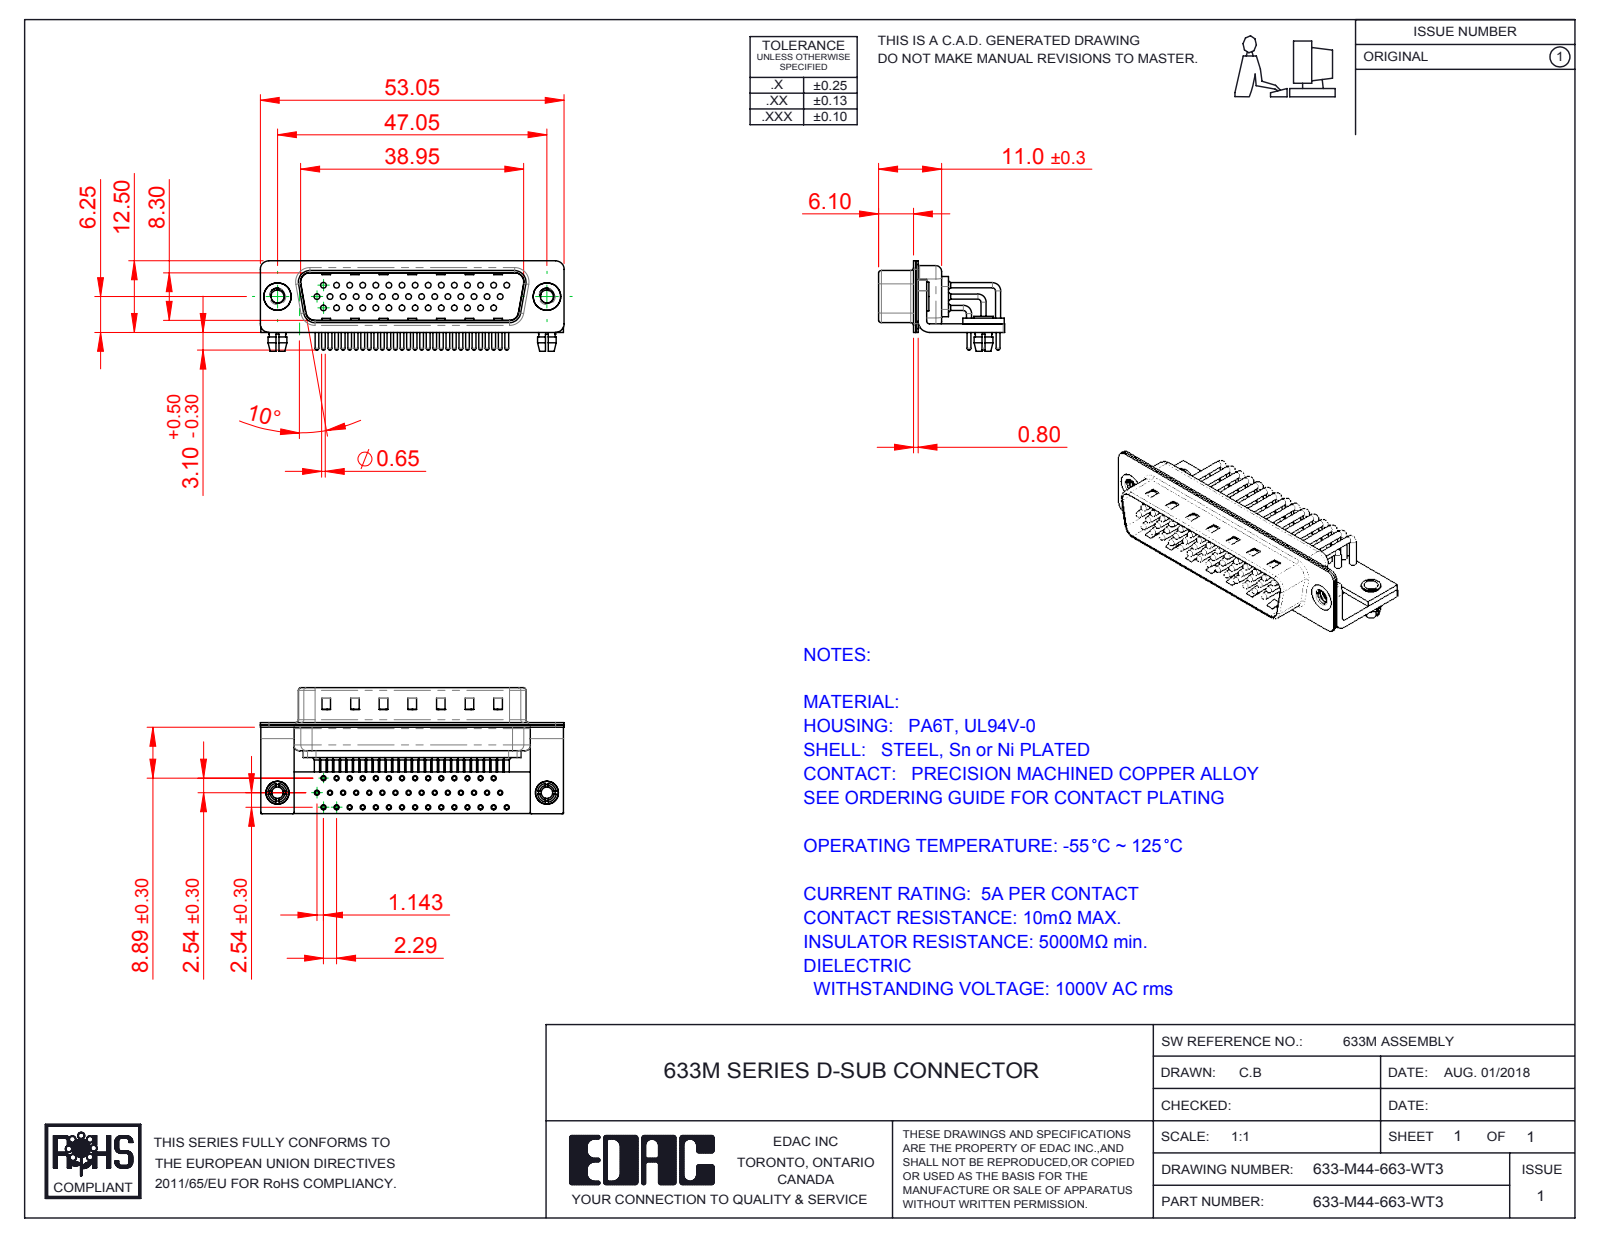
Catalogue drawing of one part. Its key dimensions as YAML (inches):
part_name: "633M Board Lock; 633M Stabilizer Board_44 Contacts; 633M Stabilizer Bracket; 633M 4-40 Threaded Rivet_Stabilizer (+7 more)"
step_written_by: "SolidWorks 2016 (CONFIG_CONTROL_DESIGN)"
units: inches
bodies: {solids: 54, faces: 5446, planar: 3061, cylindrical: 1863, other: 522}
overall_size: [2.089, 0.866, 0.622]
volume: 0.232
surface_area: 18.37
round_holes:
  - {diameter: 0.079, count: 46}
  - {diameter: 0.035, count: 44}
  - {diameter: 0.039, count: 44}
  - {diameter: 0.067, count: 44}
  - {diameter: 0.089, count: 2}
  - {diameter: 0.098, count: 2}
  - {diameter: 0.126, count: 2}
  - {diameter: 0.157, count: 2}
  - {diameter: 0.189, count: 2}
round_bosses_or_shafts:
  - {diameter: 0.035, count: 45}
  - {diameter: 0.059, count: 44}
  - {diameter: 0.026, count: 44}
  - {diameter: 0.197, count: 2}
  - {diameter: 0.193, count: 2}
  - {diameter: 0.157, count: 2}
  - {diameter: 0.134, count: 2}
  - {diameter: 0.13, count: 2}
partial_cylinders:
  - {radius: 0.04, count: 44}
  - {radius: 0.01, count: 16}
  - {radius: 0.059, count: 16}
  - {radius: 0.079, count: 13}
  - {radius: 0.02, count: 9}
  - {radius: 0.063, count: 8}
  - {radius: 0.024, count: 4}
  - {radius: 0.026, count: 4}
face_to_face_distances: [0.016, 0.059, 0.033, 0.049, 0.039, 0.075, 0.409, 0.031, 0.376, 0.327]
hole_center_spacings: [0.09, 0.09, 0.18, 0.27, 0.156, 0.45, 0.324, 0.63]
